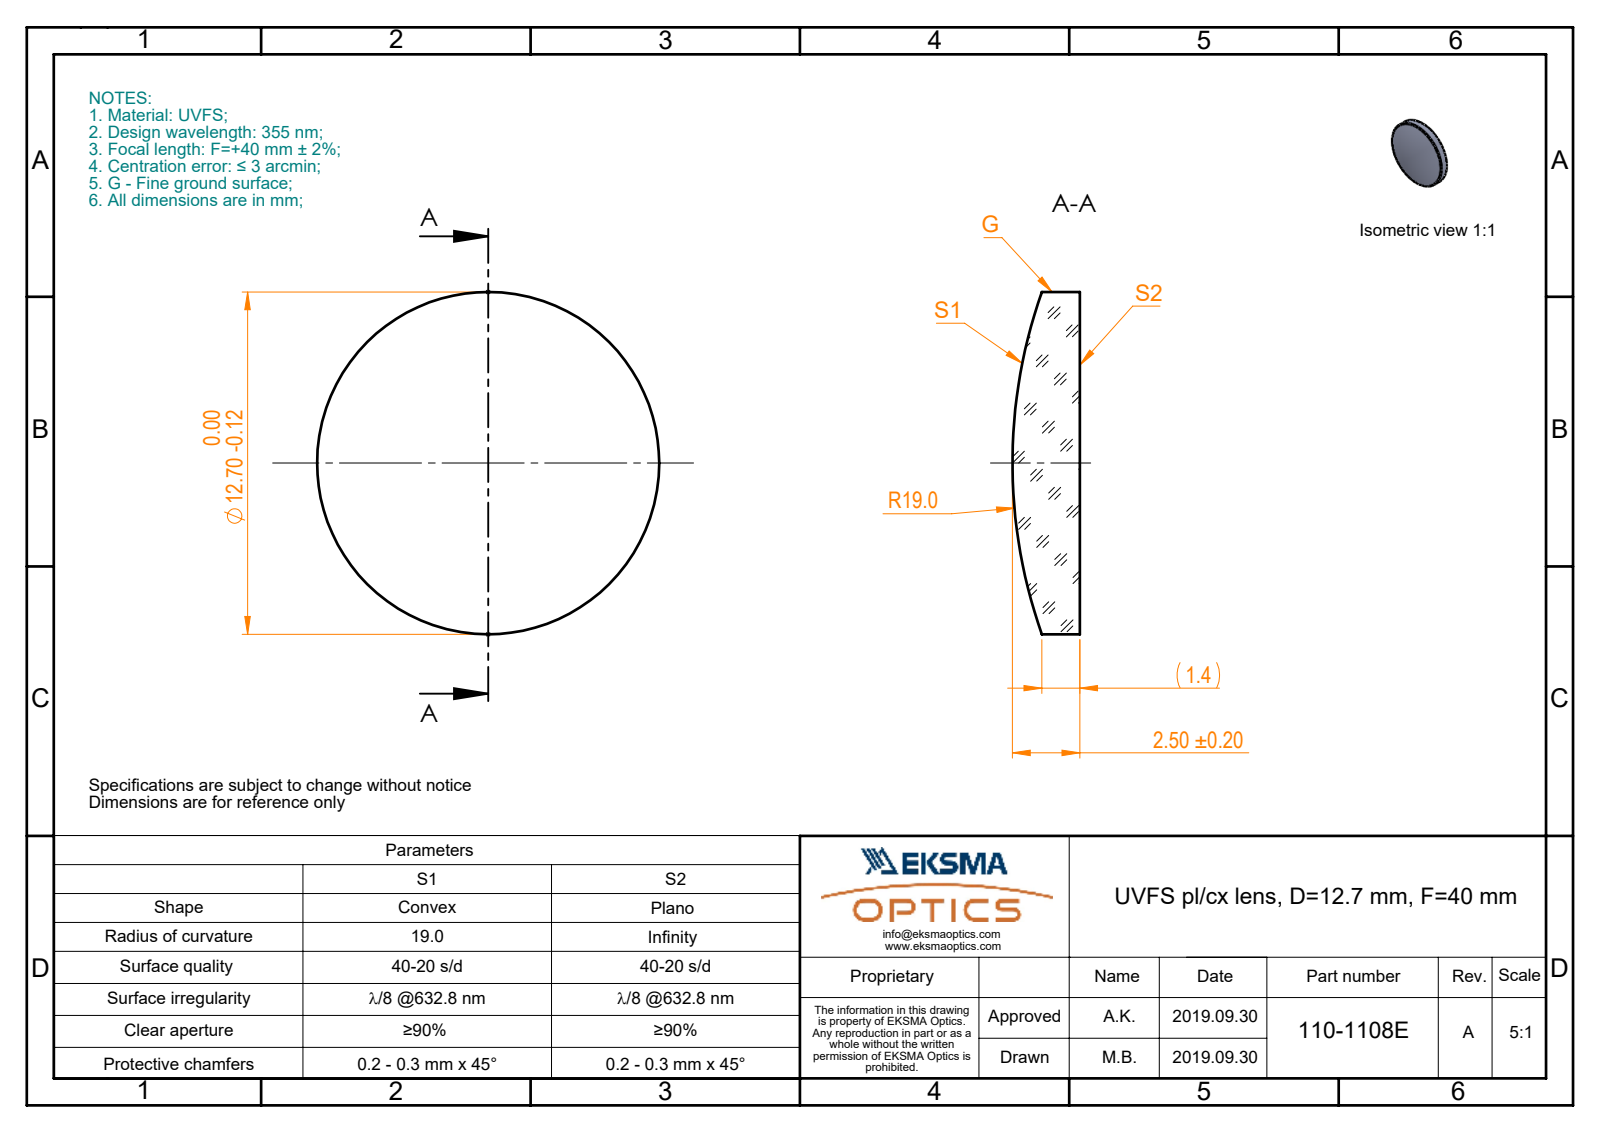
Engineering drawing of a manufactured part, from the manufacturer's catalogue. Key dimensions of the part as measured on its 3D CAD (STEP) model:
Part name (STEP PRODUCT): 110-1108E UVFS pl-cx 12.7 F40
STEP written by: SolidWorks 2019 (CONFIG_CONTROL_DESIGN)
Units: millimetres
Bodies: 1 solid, 4 faces (1 planar, 2 cylindrical, 1 other)
Overall size (bounding box): 12.7 × 12.7 × 2.5
Volume: 248 mm³ · Surface area: 313 mm²
Round bosses / shafts (diameter × count): ⌀12.7 ×1
